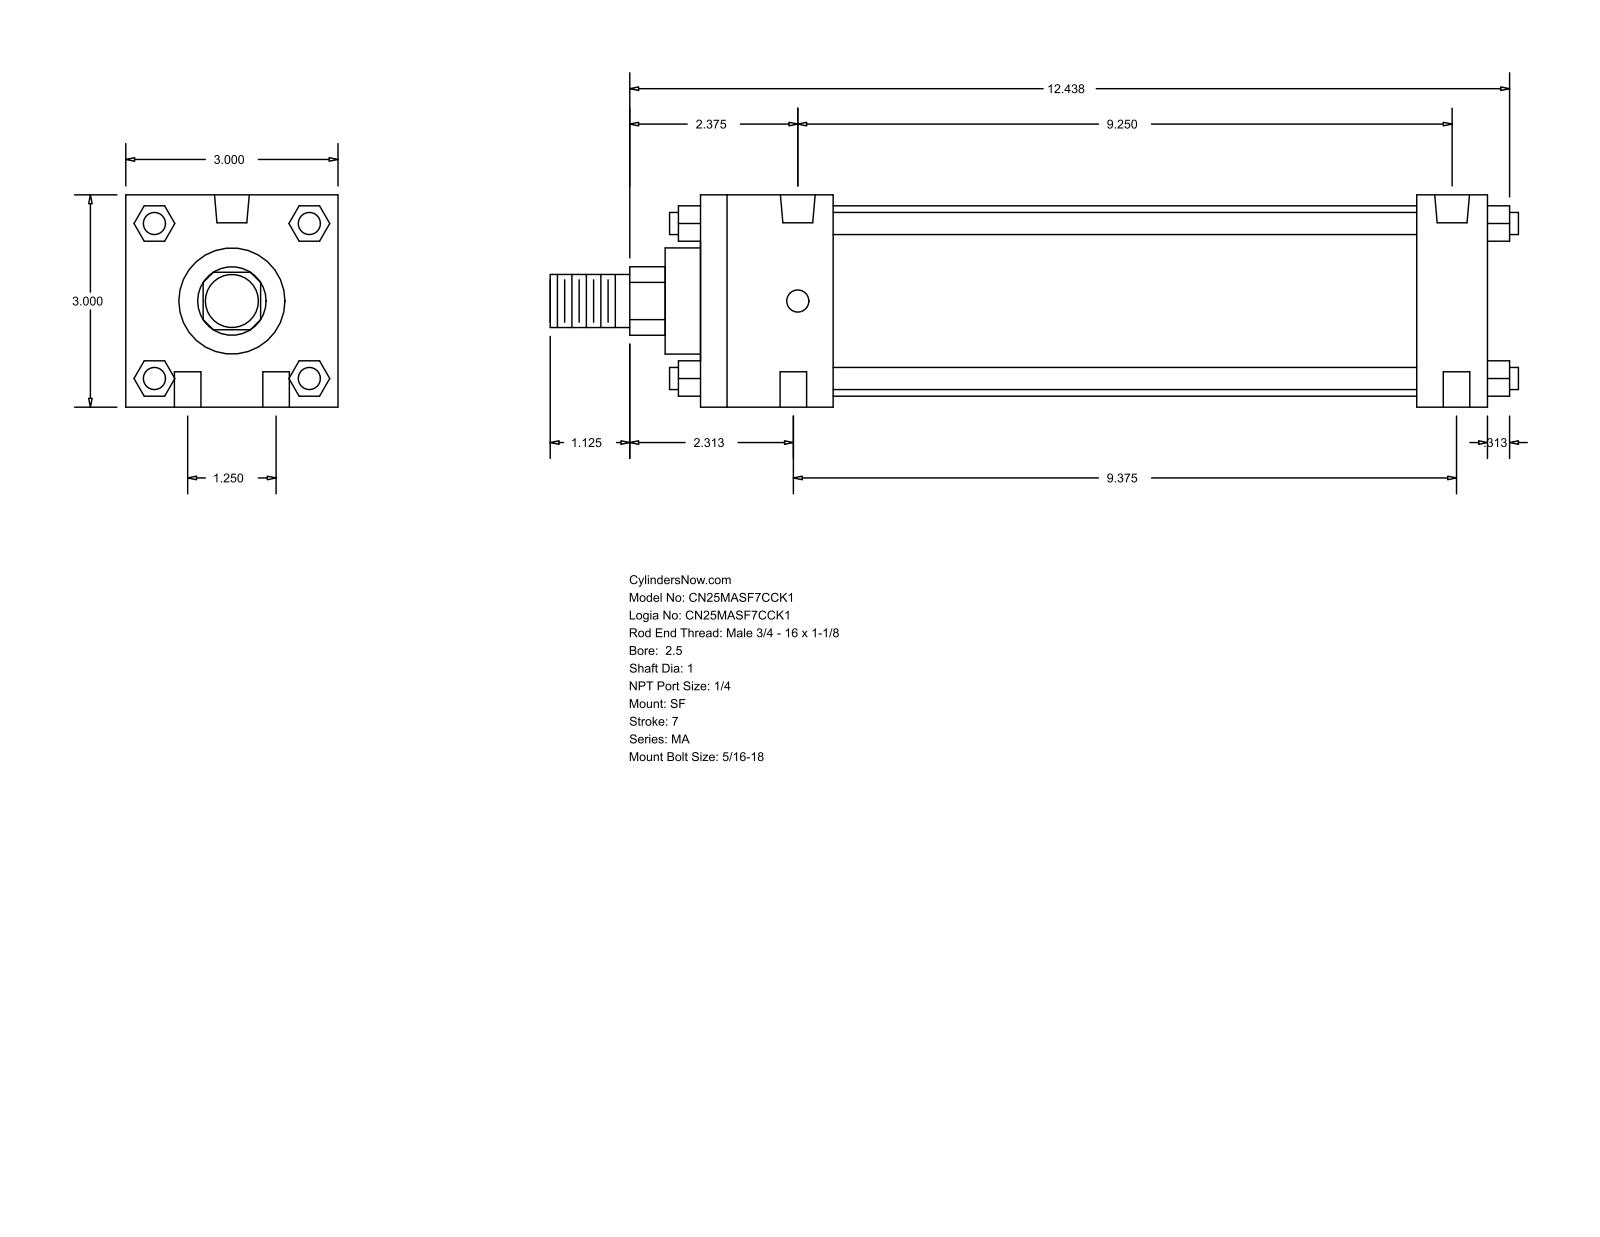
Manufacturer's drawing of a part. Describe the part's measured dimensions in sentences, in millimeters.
The part is named "MA_SF__0250_1". Its 3-D file was written by "GSSL Pune (CONFIG_CONTROL_DESIGN)". It is 0 solids with 124 faces: 94 planar, 30 cylindrical and 0 other. Overall it measures 347.66 by 76.2 by 76.2 millimeters. Round holes: 4 of diameter 9.53, 2 of diameter 7.94, 2 of diameter 12.49. Round bosses or shafts: 4 of diameter 7.94, 1 of diameter 68.33, 1 of diameter 38.1, 1 of diameter 25.4, 1 of diameter 19.05. Partial cylindrical surfaces (rounded edges, fillets, slot ends): 1 of radius 12.29. The main face-to-face distances are 76.2, 282.58, 12.7, 257.17, 25.41, 47.63, 209.54, 234.95, 27.81, 48.17. The hole center spacings are 15.96, 237.06, 31.76, 234.94, 238.12, 240.23.
